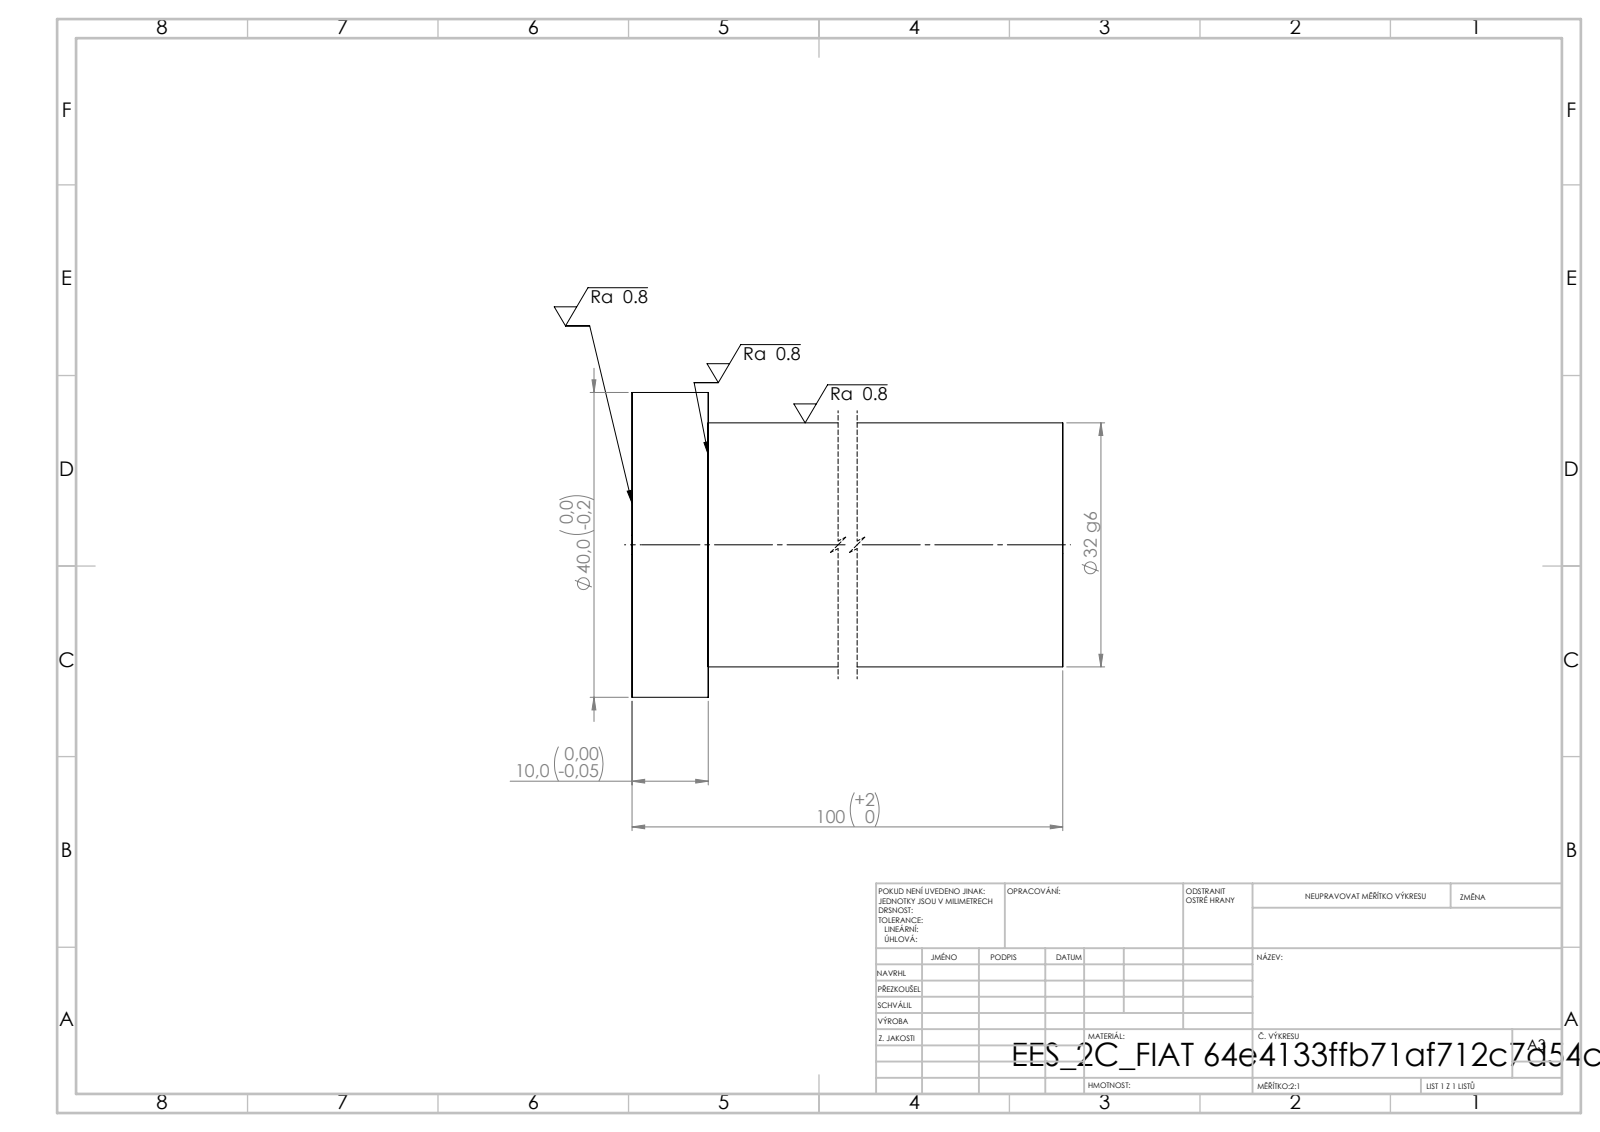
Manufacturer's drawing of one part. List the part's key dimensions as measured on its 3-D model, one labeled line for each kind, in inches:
STEP written by: SolidWorks 2019 (CONFIG_CONTROL_DESIGN)
Units: inches
Bodies: 1 solid, 7 faces (3 planar, 4 cylindrical, 0 other)
Overall size (bounding box): 3.937 × 1.575 × 1.575
Volume: 5.184 in³ · Surface area: 19.87 in²
Round bosses / shafts (diameter × count): ⌀1.575 ×1, ⌀1.26 ×1
Main face-to-face distances: 3.937, 0.394, 3.543
